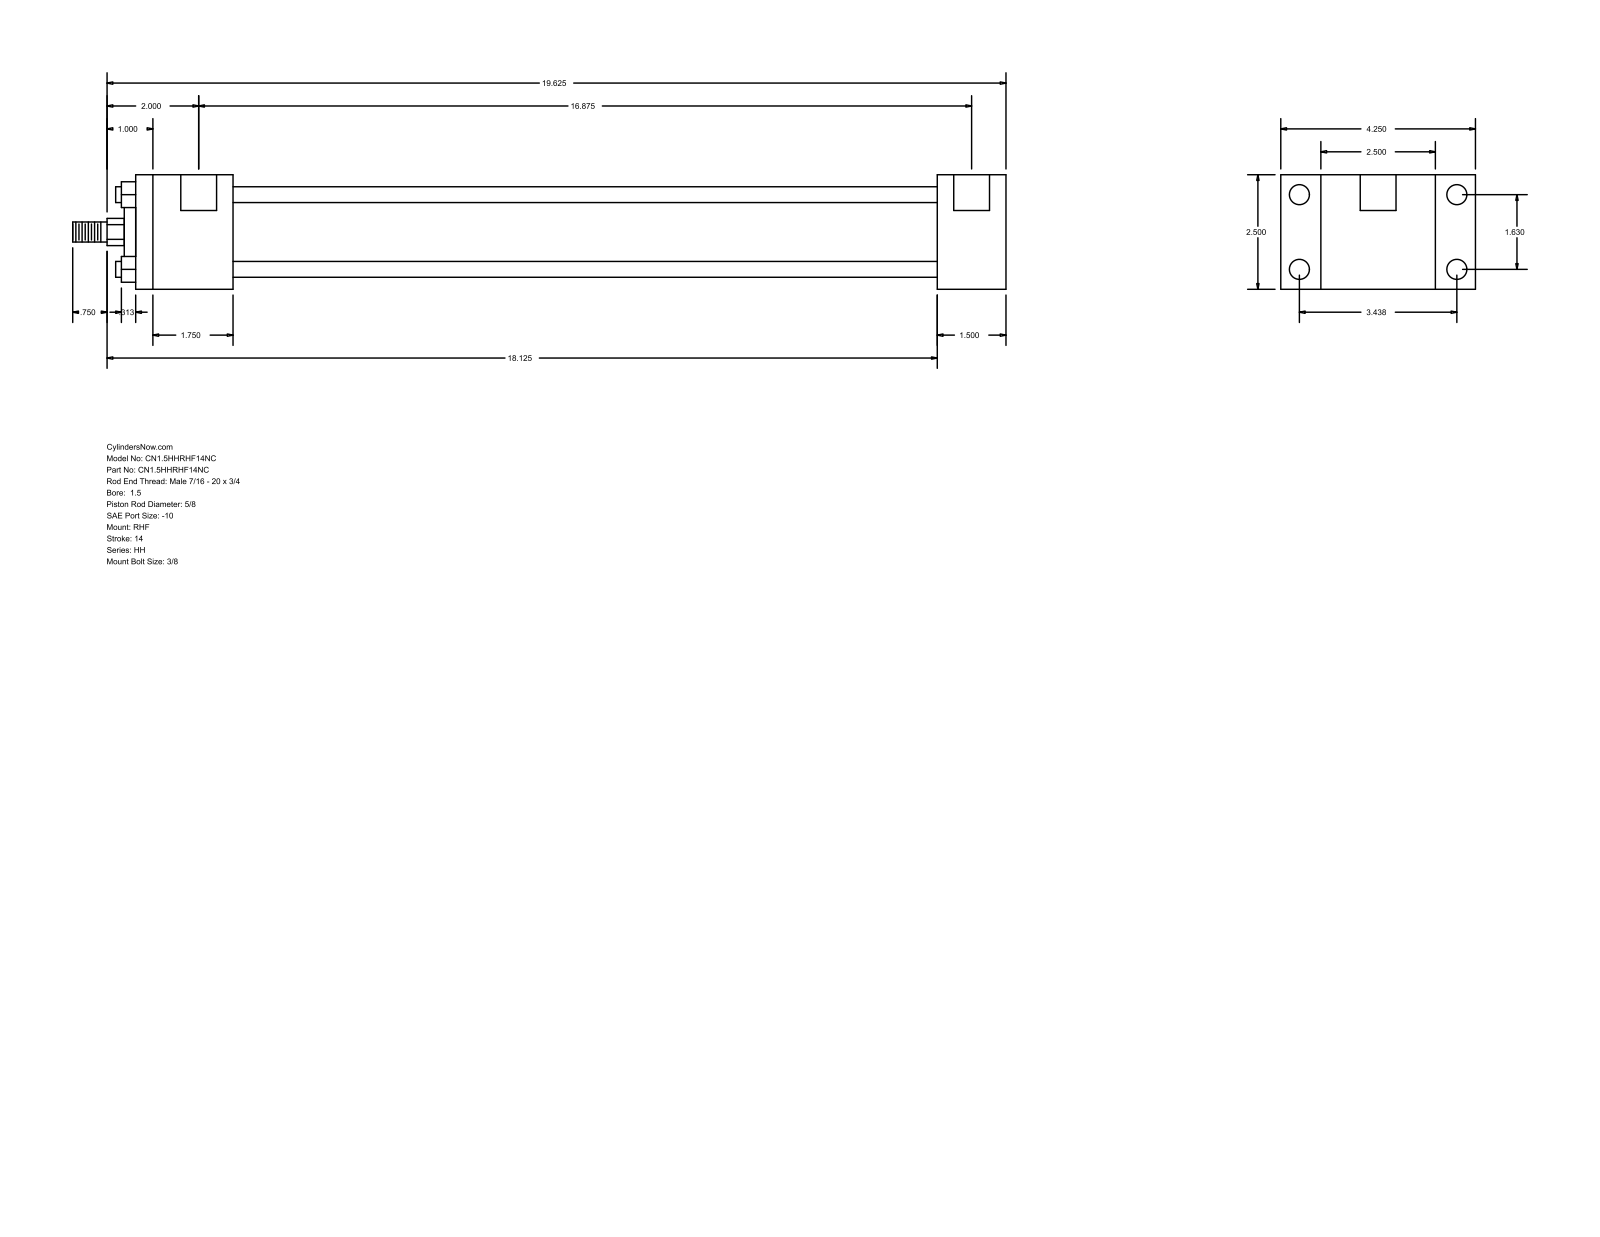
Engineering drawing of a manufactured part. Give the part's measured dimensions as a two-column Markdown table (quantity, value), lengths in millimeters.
| quantity | value |
| --- | --- |
| part name | HH_RHF__0150_0.625 |
| STEP written by | GSSL Pune (CONFIG_CONTROL_DESIGN) |
| units | millimeters |
| bodies | 0 solids, 88 faces (60 planar, 28 cylindrical, 0 other) |
| overall size | 517.52 × 107.95 × 63.5 |
| round holes (diameter × count) | 5.56 × 4, 11.13 × 4, 19.84 × 2 |
| round bosses / shafts (diameter × count) | 8.76 × 4, 44.45 × 1, 28.57 × 1, 15.88 × 1, 11.11 × 1 |
| partial cylindrical surfaces (radius × count) | 7.54 × 1 |
| main face-to-face distances | 63.5, 38.1, 22.23, 85.73, 444.5, 482.6, 107.96, 53.97, 390.53, 428.63 |
| hole center spacings | 41.4, 87.32, 96.64, 431.8, 1.58, 1.59, 428.63, 430.21 |
